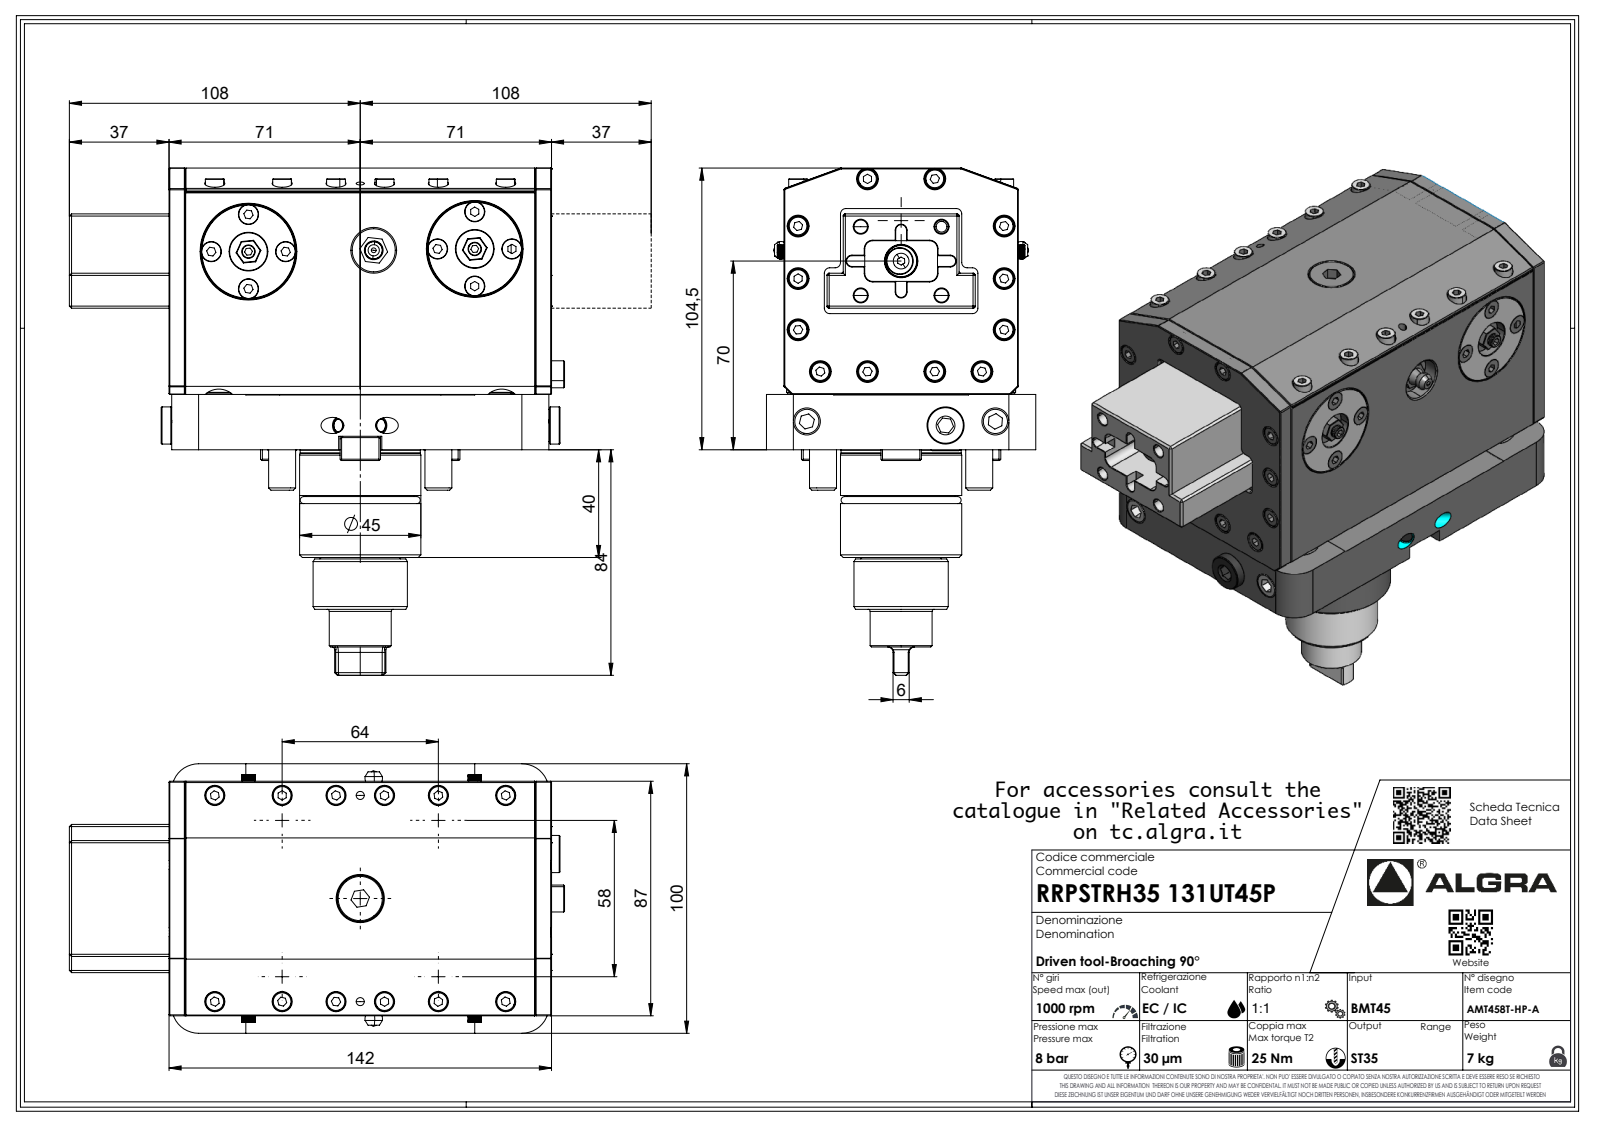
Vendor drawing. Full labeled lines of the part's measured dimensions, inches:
Part name (STEP PRODUCT): RRPSTRH35131UT45P
STEP written by: SolidWorks 2023 (AUTOMOTIVE_DESIGN)
Units: inches
Bodies: 0 solids, 1298 faces (655 planar, 278 cylindrical, 365 other)
Overall size (bounding box): 7.409 × 7.237 × 3.937
Round holes (diameter × count): ⌀0.177 ×12, ⌀0.295 ×12, ⌀0.591 ×4, ⌀1.398 ×2, ⌀0.083 ×1, ⌀0.197 ×1, ⌀0.402 ×1, ⌀0.472 ×1
Round bosses / shafts (diameter × count): ⌀0.276 ×12, ⌀0.472 ×5, ⌀1.378 ×3, ⌀0.394 ×2, ⌀0.197 ×2, ⌀2.165 ×1, ⌀1.857 ×1, ⌀1.772 ×1
Partial cylindrical surfaces — rounded edges, fillets, slot ends (radius × count): R0.079 ×14, R0.098 ×12, R0.008 ×8, R0.02 ×8, R0.142 ×8, R0.013 ×7, R0.02 ×7, R0.146 ×7
Main face-to-face distances: 3.425, 0.799, 0.807, 4.114, 3.307, 3.315, 5.591, 0.256, 3.681, 0.039
Hole centre spacings: 3.012, 0.494, 0.689, 0.691, 0.748, 0.768, 0.984, 1.182
